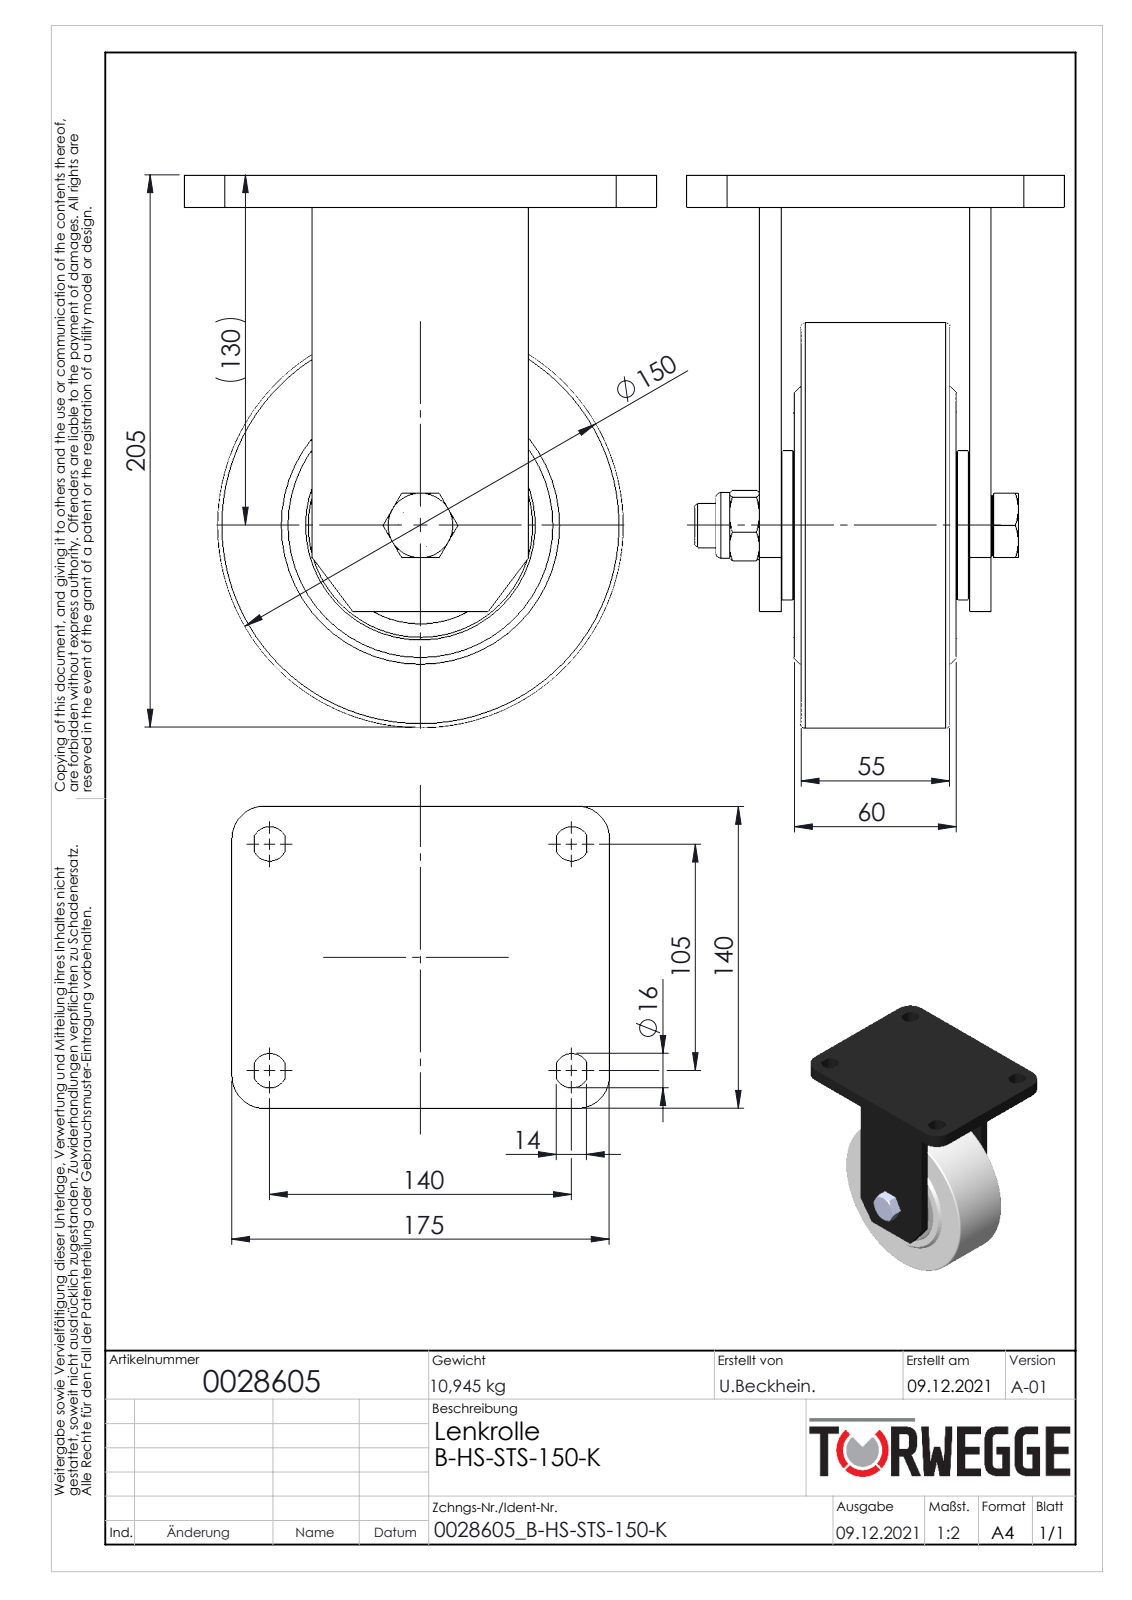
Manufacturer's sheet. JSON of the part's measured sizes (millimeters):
{"part_name": "0028605", "step_written_by": "SolidWorks 2020 (AUTOMOTIVE_DESIGN)", "units": "millimeters", "bodies": {"solids": 0, "faces": 195, "planar": 63, "cylindrical": 62, "other": 70}, "overall_size": [205, 175, 140], "round_holes": [[14, 1], [16, 1], [16.3, 1], [18.29, 1], [45, 1], [48, 1], [73, 1], [85, 1]], "round_bosses_or_shafts": [[150, 1], [57, 1], [55, 1], [24, 1]], "partial_cylinders_radius": [[8, 4], [15, 4]], "face_to_face_distances": [78, 8, 12, 15.5, 70.5, 7.5, 62.5, 70, 86, 13]}
